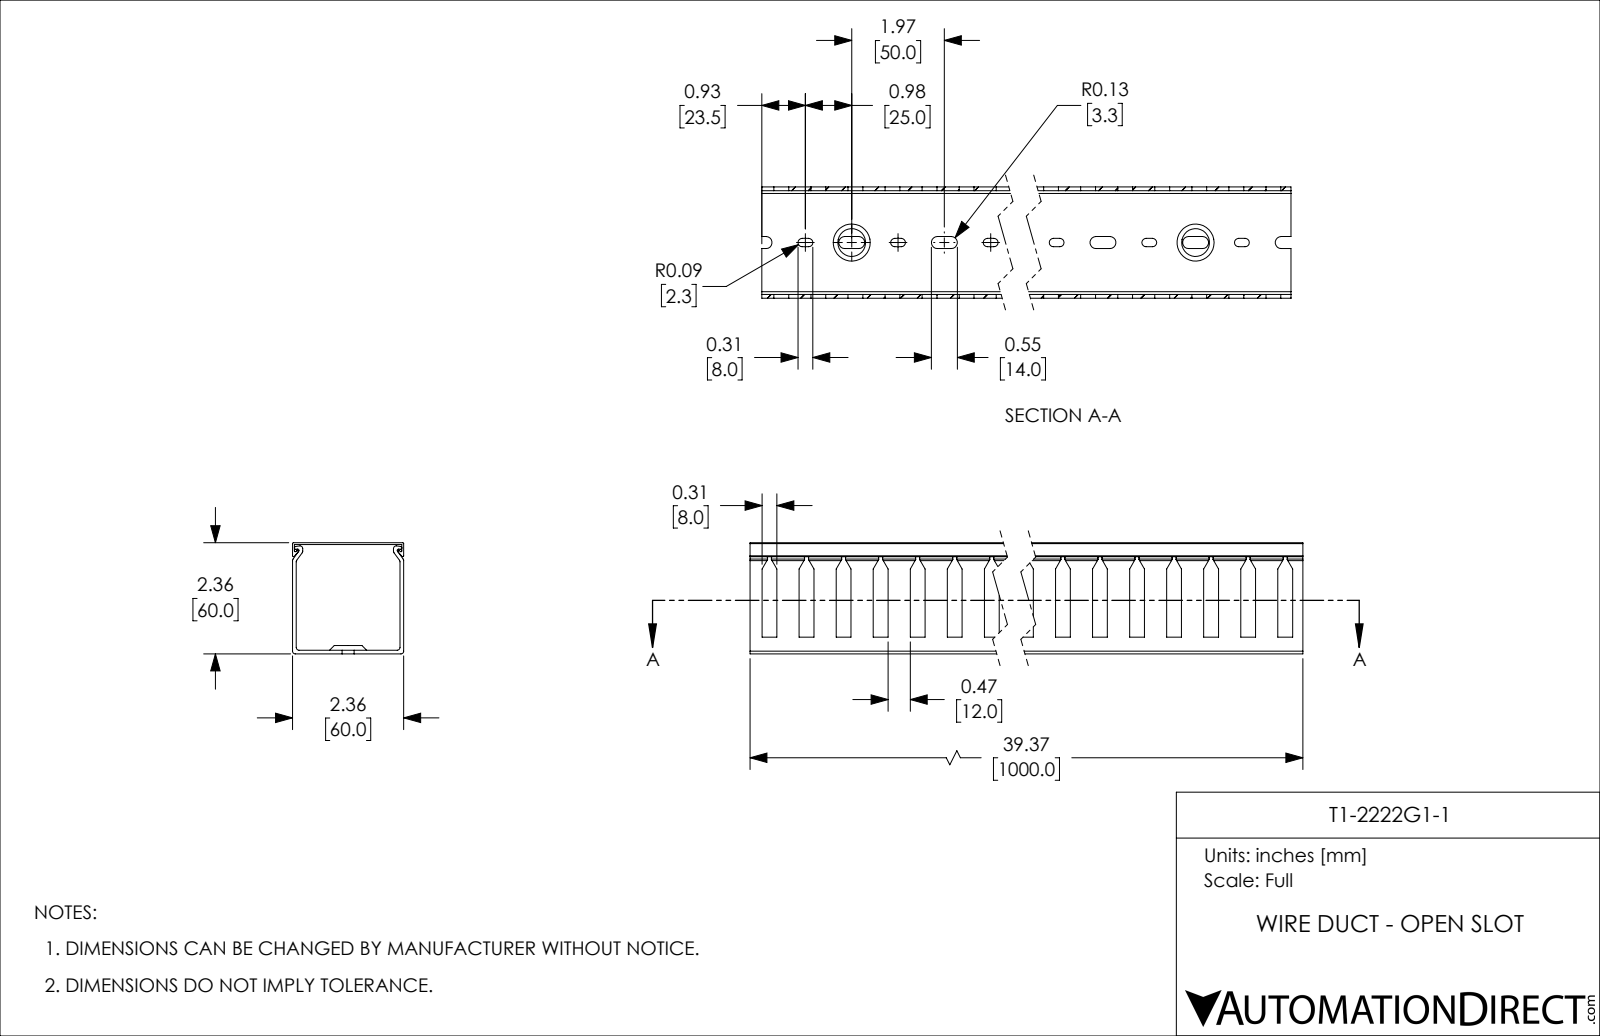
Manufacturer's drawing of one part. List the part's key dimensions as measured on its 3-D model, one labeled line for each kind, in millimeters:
Part name (STEP PRODUCT): T1-2222G1-1
STEP written by: SolidWorks 2021 (CONFIG_CONTROL_DESIGN)
Units: millimetres
Bodies: 2 solids, 775 faces (444 planar, 311 cylindrical, 20 other)
Overall size (bounding box): 1000 × 60 × 60
Volume: 419 861 mm³ · Surface area: 500 923 mm²
Partial cylindrical surfaces — rounded edges, fillets, slot ends (radius × count): R2.25 ×40, R3.25 ×40, R1.5 ×12, R0.5 ×8, R0.75 ×6
Main face-to-face distances: 2, 58, 60, 1, 59, 57, 56, 4.5, 54.5, 5.5
